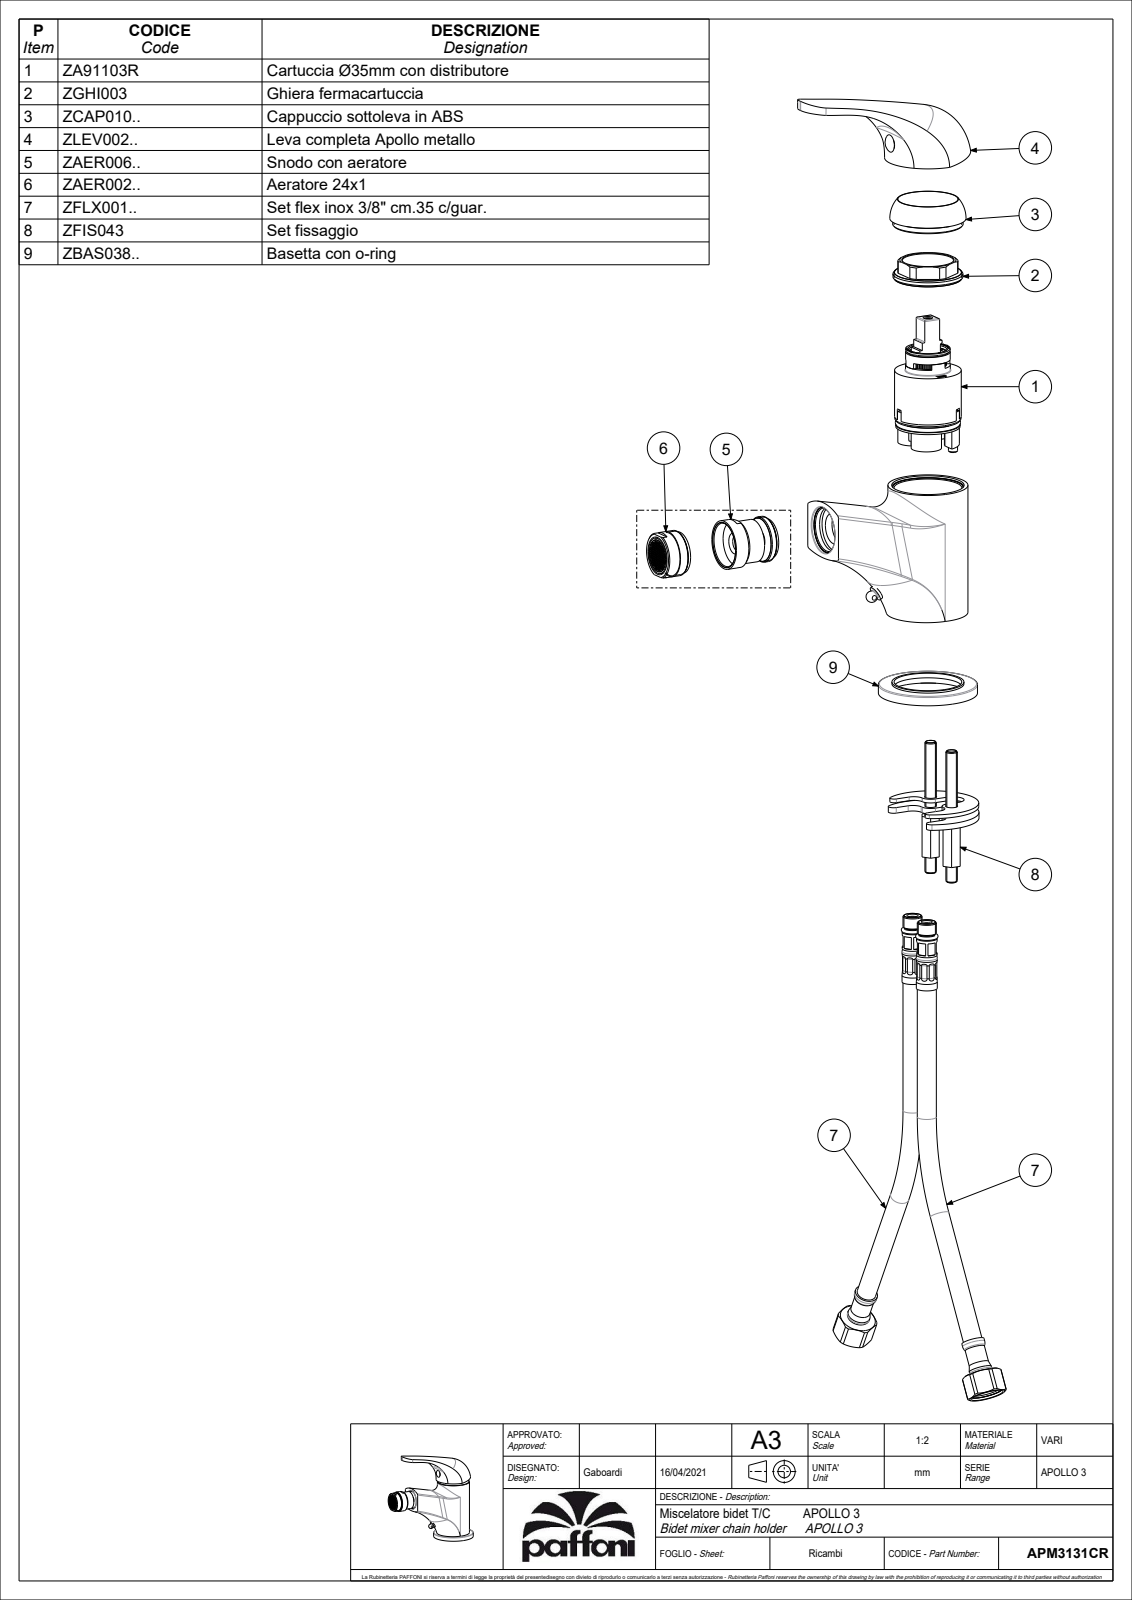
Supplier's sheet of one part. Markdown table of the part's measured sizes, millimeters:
| quantity | value |
| --- | --- |
| part name | APM3131CR |
| STEP written by | CREO PARAMETRIC BY PTC INC, 2020044 (CONFIG_CONTROL_DESIGN) |
| units | millimeters |
| bodies | 2 solids, 2670 faces (2042 planar, 352 cylindrical, 276 other) |
| overall size | 118.2 × 118 × 52 |
| volume | 112 092 mm³ |
| surface area | 79 399 mm² |
| round holes (diameter × count) | 9 × 5, 5 × 3, 8 × 3, 12 × 3, 4 × 2, 7 × 2, 11 × 2, 2.5 × 1, 3.3 × 1, 6 × 1, 15.5 × 1, 16 × 1 |
| round bosses / shafts (diameter × count) | 8 × 2, 52 × 1, 42.6 × 1, 42 × 1, 37.8 × 1, 34.8 × 1, 33.8 × 1, 32.2 × 1 |
| partial cylindrical surfaces (radius × count) | 0.5 × 42, 1 × 12, 0.15 × 11, 0.3 × 9, 2 × 8, 5 × 4, 7 × 4, 4.5 × 2 |
| main face-to-face distances | 3, 5, 2.5, 12, 0.5, 1.5, 1.7, 32.5, 9, 3.5 |
| hole center spacings | 13.6, 0.5, 0.71, 1.12, 8.51, 8.6, 9.01, 11.18 |
